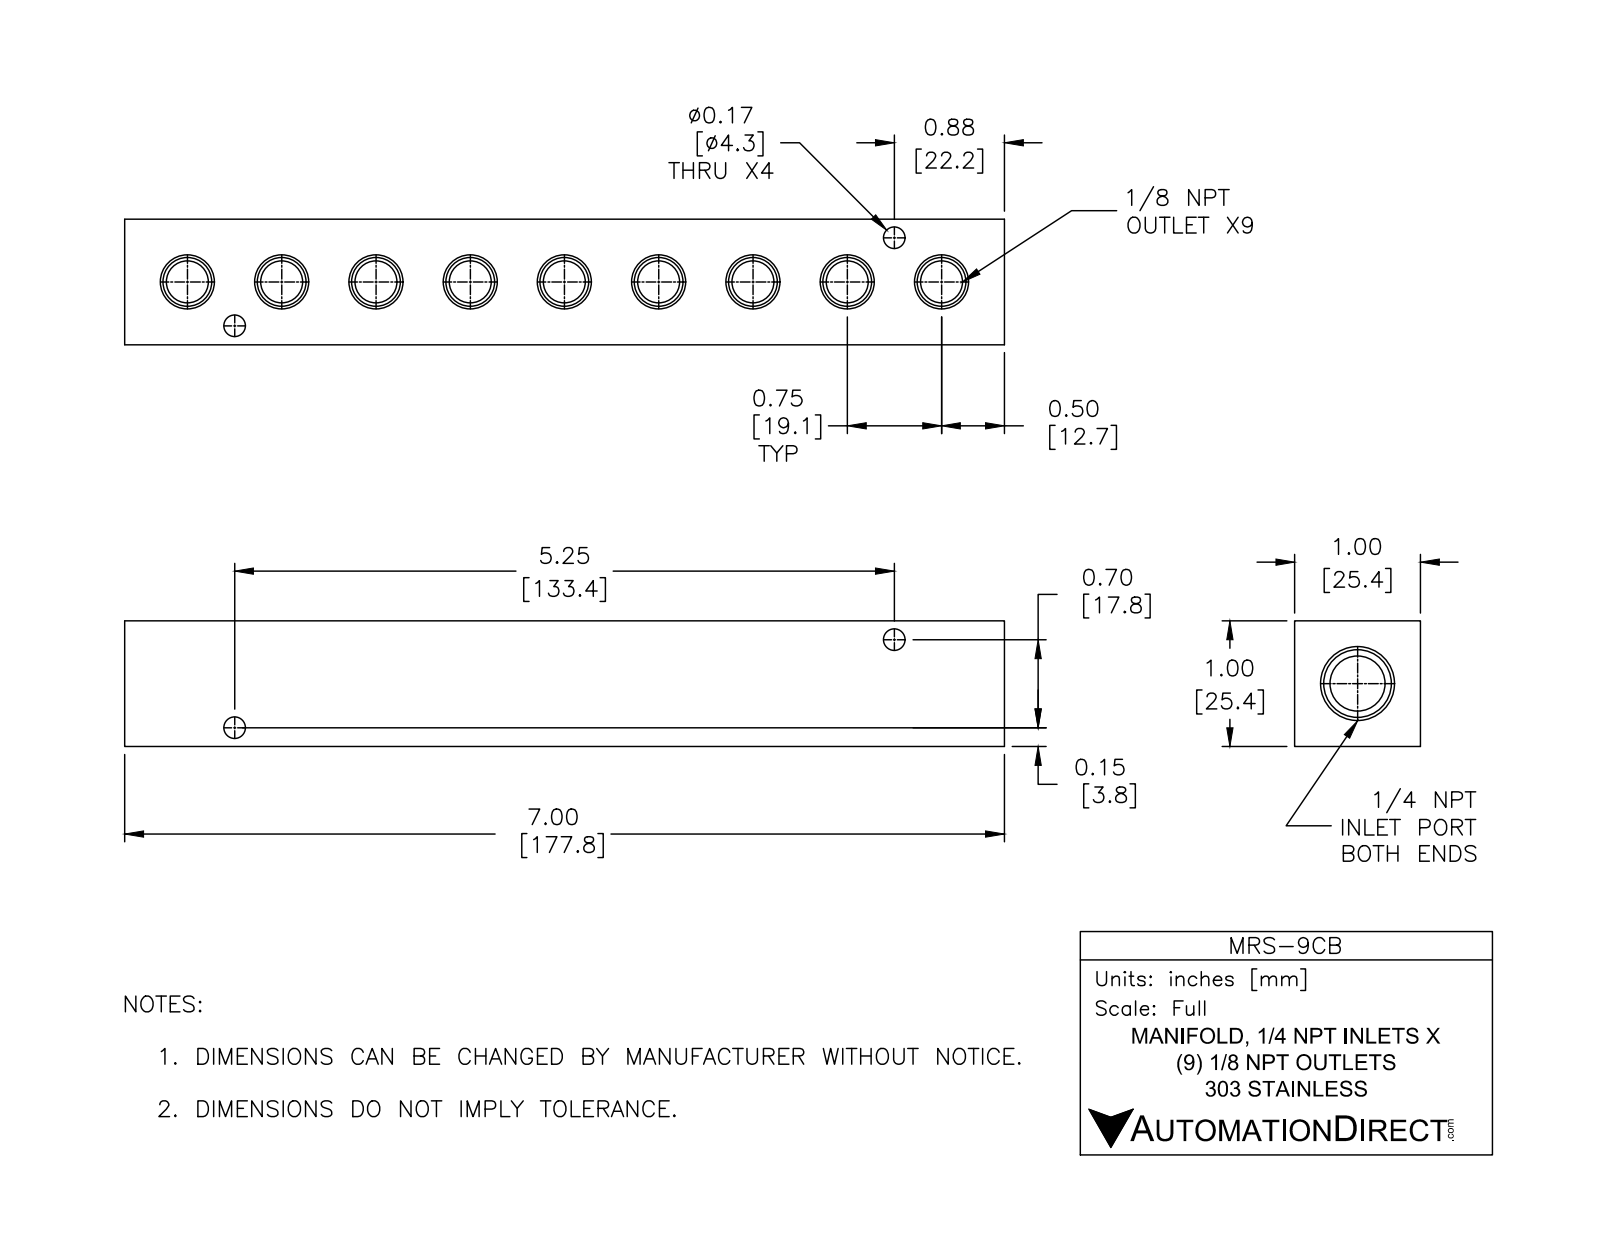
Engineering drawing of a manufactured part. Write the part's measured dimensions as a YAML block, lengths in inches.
part_name: "MRS-9CB"
step_written_by: "SolidWorks 2015 (CONFIG_CONTROL_DESIGN)"
units: inches
bodies: {solids: 1, faces: 96, planar: 17, cylindrical: 35, other: 44}
overall_size: [7, 1, 1]
volume: 5.482
surface_area: 42.79
round_holes:
  - {diameter: 0.332, count: 7}
  - {diameter: 0.17, count: 4}
  - {diameter: 0.438, count: 1}
partial_cylinders:
  - {radius: 0.166, count: 2}
face_to_face_distances: [1, 7, 0.73, 0.27, 0.39, 6.61, 6.22]
hole_center_spacings: [0.75, 1.5, 2.25, 3, 0.513, 1.178, 1.907, 2.648]
